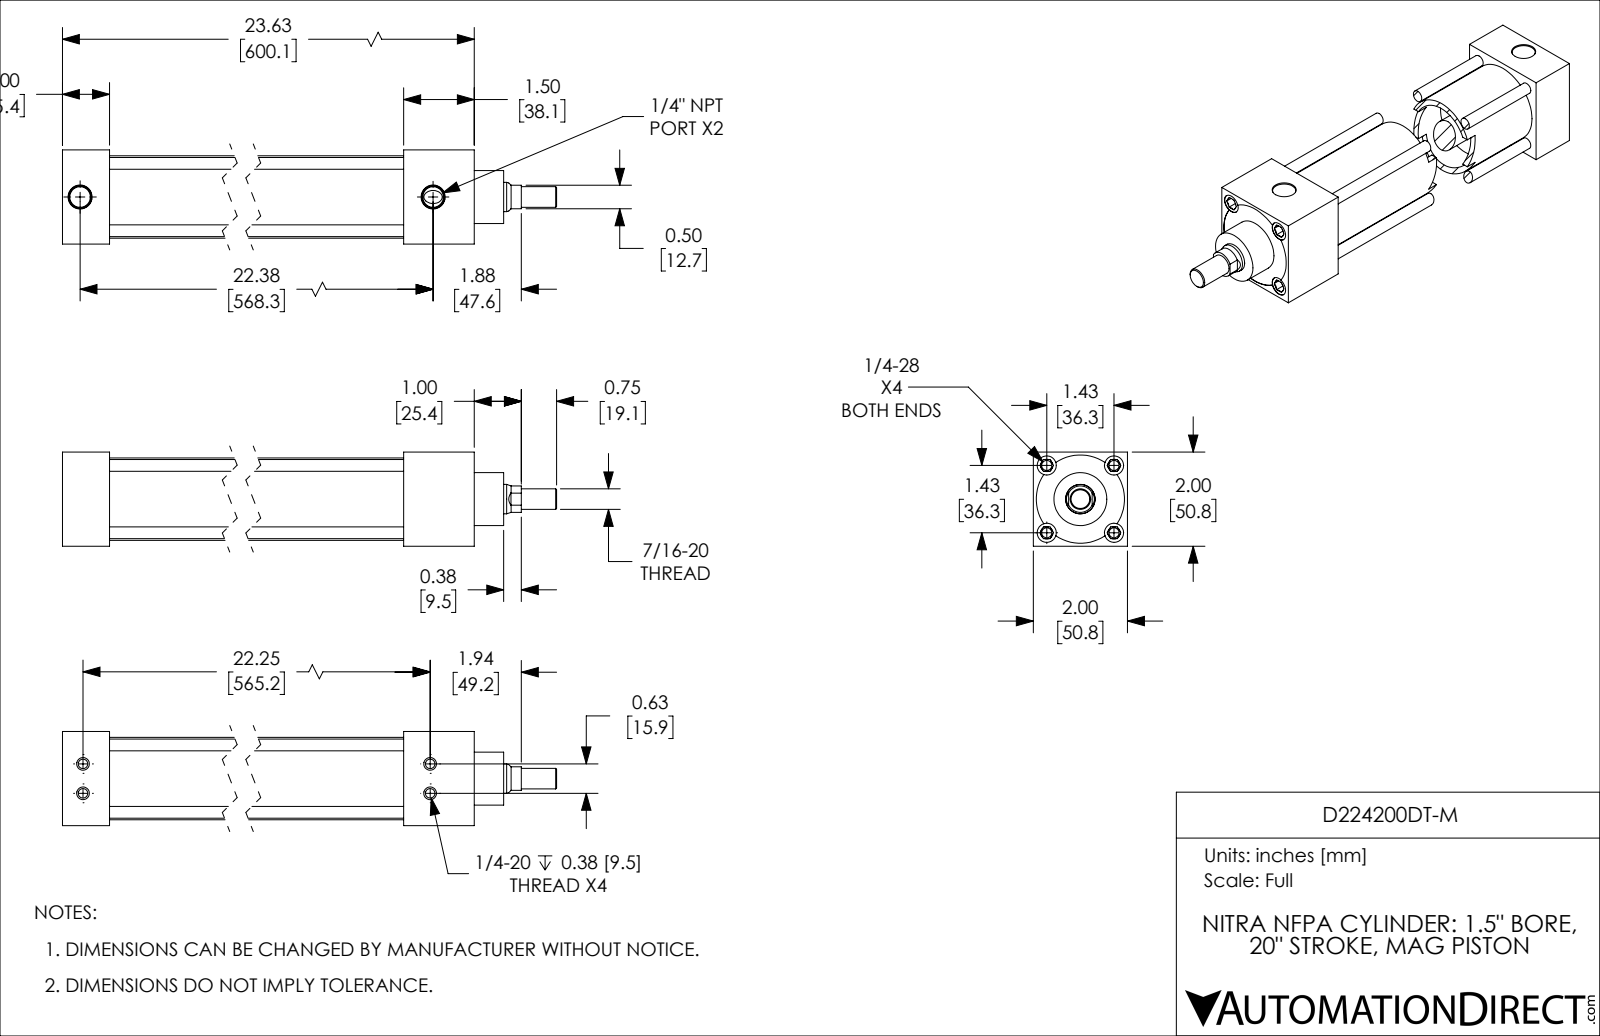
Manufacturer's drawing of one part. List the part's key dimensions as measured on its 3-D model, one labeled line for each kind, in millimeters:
Part name (STEP PRODUCT): D224200DT-M; D224200DT-M_BODY; D224200DT-M_PISTON_KK1
STEP written by: SolidWorks 2019 (CONFIG_CONTROL_DESIGN)
Units: millimetres
Bodies: 2 solids, 203 faces (58 planar, 65 cylindrical, 80 other)
Overall size (bounding box): 644.5 × 50.8 × 50.8
Volume: 589 800 mm³ · Surface area: 247 500 mm²
Round holes (diameter × count): ⌀5.1 ×4, ⌀5.4 ×4, ⌀10.3 ×4, ⌀11.1 ×2, ⌀15.9 ×1, ⌀38.1 ×1
Round bosses / shafts (diameter × count): ⌀6.4 ×4, ⌀44.5 ×1, ⌀38.1 ×1, ⌀28.6 ×1, ⌀15.8 ×1, ⌀11.1 ×1
Partial cylindrical surfaces — rounded edges, fillets, slot ends (radius × count): R7.1 ×1, R23.8 ×1
Main face-to-face distances: 50.8, 25.4, 562, 536.6, 54, 599.9, 574.5, 38, 28.6, 508
Hole centre spacings: 8.1, 25.7, 36.3, 15.9, 51.4, 565.2, 565.4, 566.8
